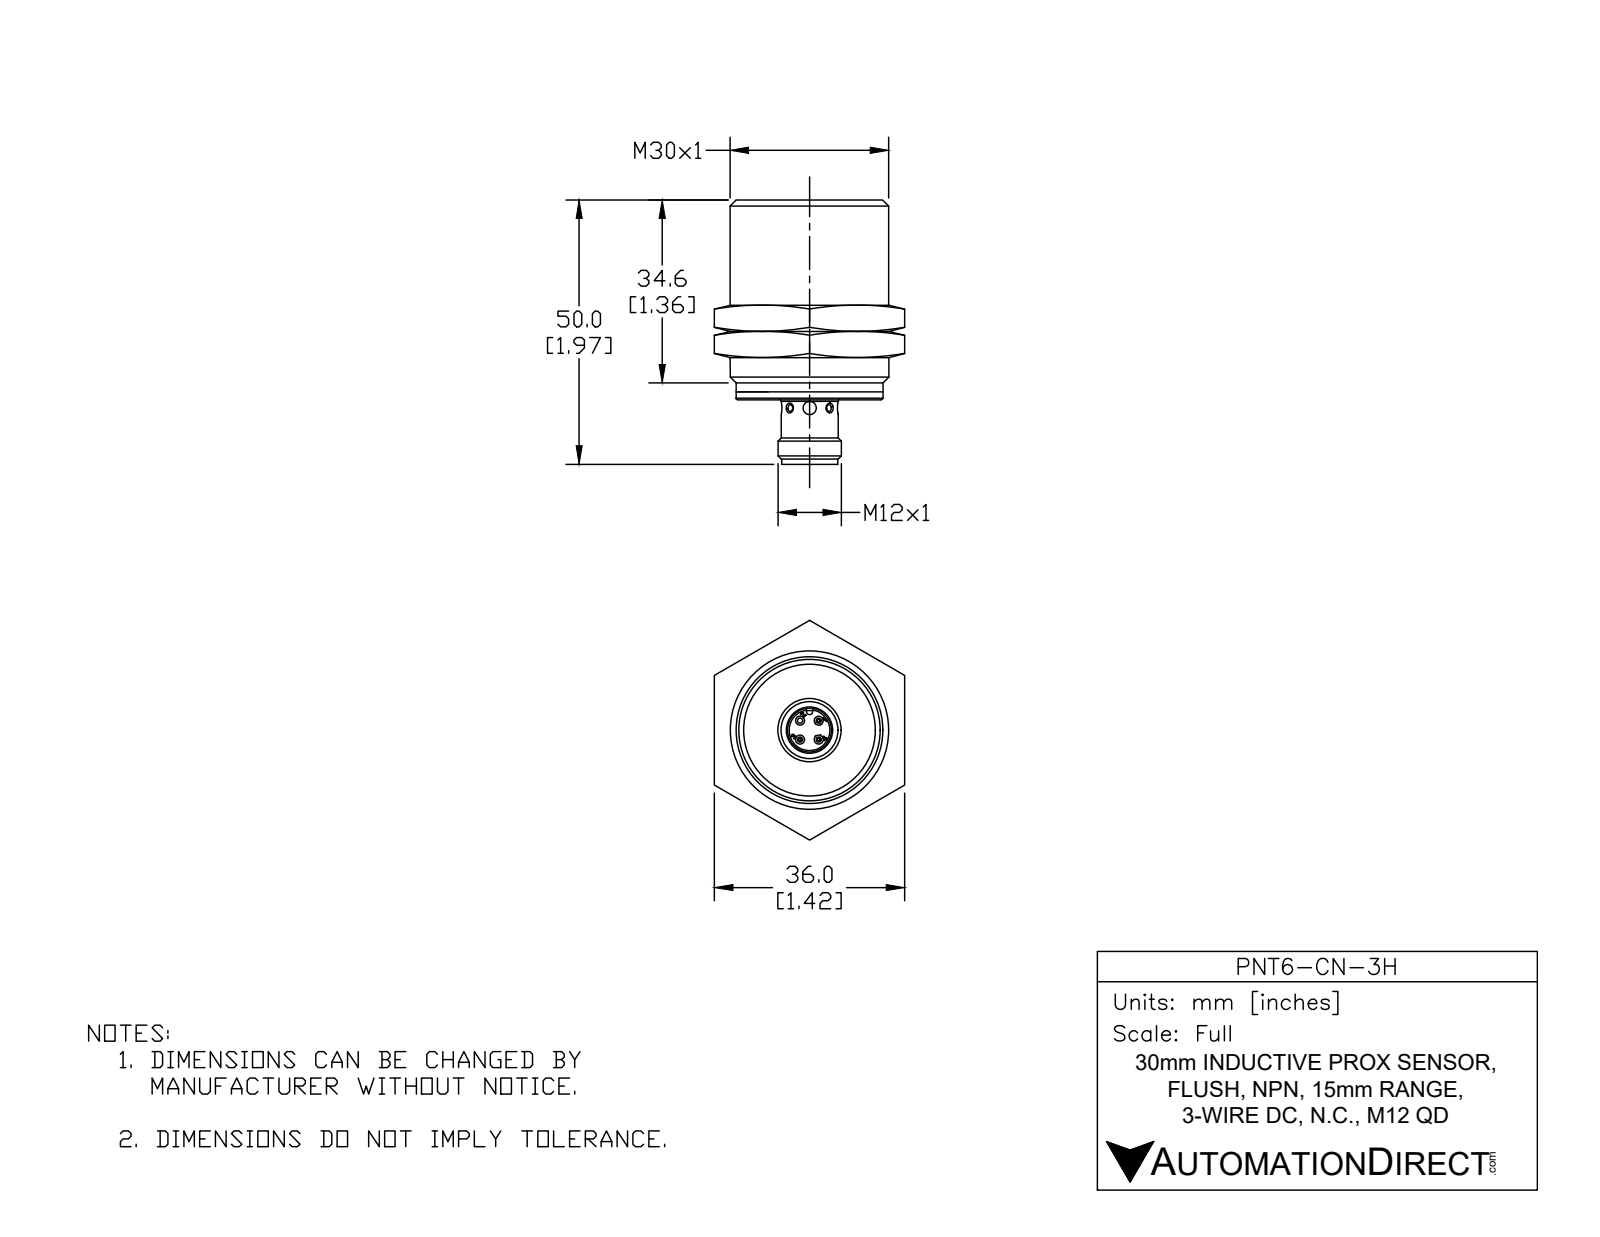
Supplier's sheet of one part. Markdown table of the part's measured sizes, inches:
| quantity | value |
| --- | --- |
| part name | PNT6-CN-3H |
| STEP written by | SolidWorks 2017 (AUTOMOTIVE_DESIGN) |
| units | inches |
| bodies | 1 solid, 515 faces (161 planar, 130 cylindrical, 224 other) |
| overall size | 1.969 × 1.181 × 1.181 |
| volume | 1.573 in³ |
| surface area | 12.79 in² |
| round holes (diameter × count) | 0.043 × 3, 0.04 × 2, 0.098 × 2, 0.038 × 1, 0.04 × 1, 0.323 × 1, 0.327 × 1, 0.394 × 1, 1.047 × 1, 1.076 × 1, 1.089 × 1 |
| round bosses / shafts (diameter × count) | 0.039 × 9, 1.181 × 1, 1.094 × 1, 1.083 × 1, 1.074 × 1, 1.044 × 1, 0.878 × 1, 0.472 × 1 |
| partial cylindrical surfaces (radius × count) | 0.004 × 12, 0.02 × 8, 0.03 × 3, 0.039 × 3, 0.024 × 1, 0.031 × 1 |
| main face-to-face distances | 0.126, 1.488, 1.362, 0.037, 0.089, 1.451, 0.098, 1.461, 0.028, 0.024 |
| hole center spacings | 0.098, 0.139, 0.197 |
